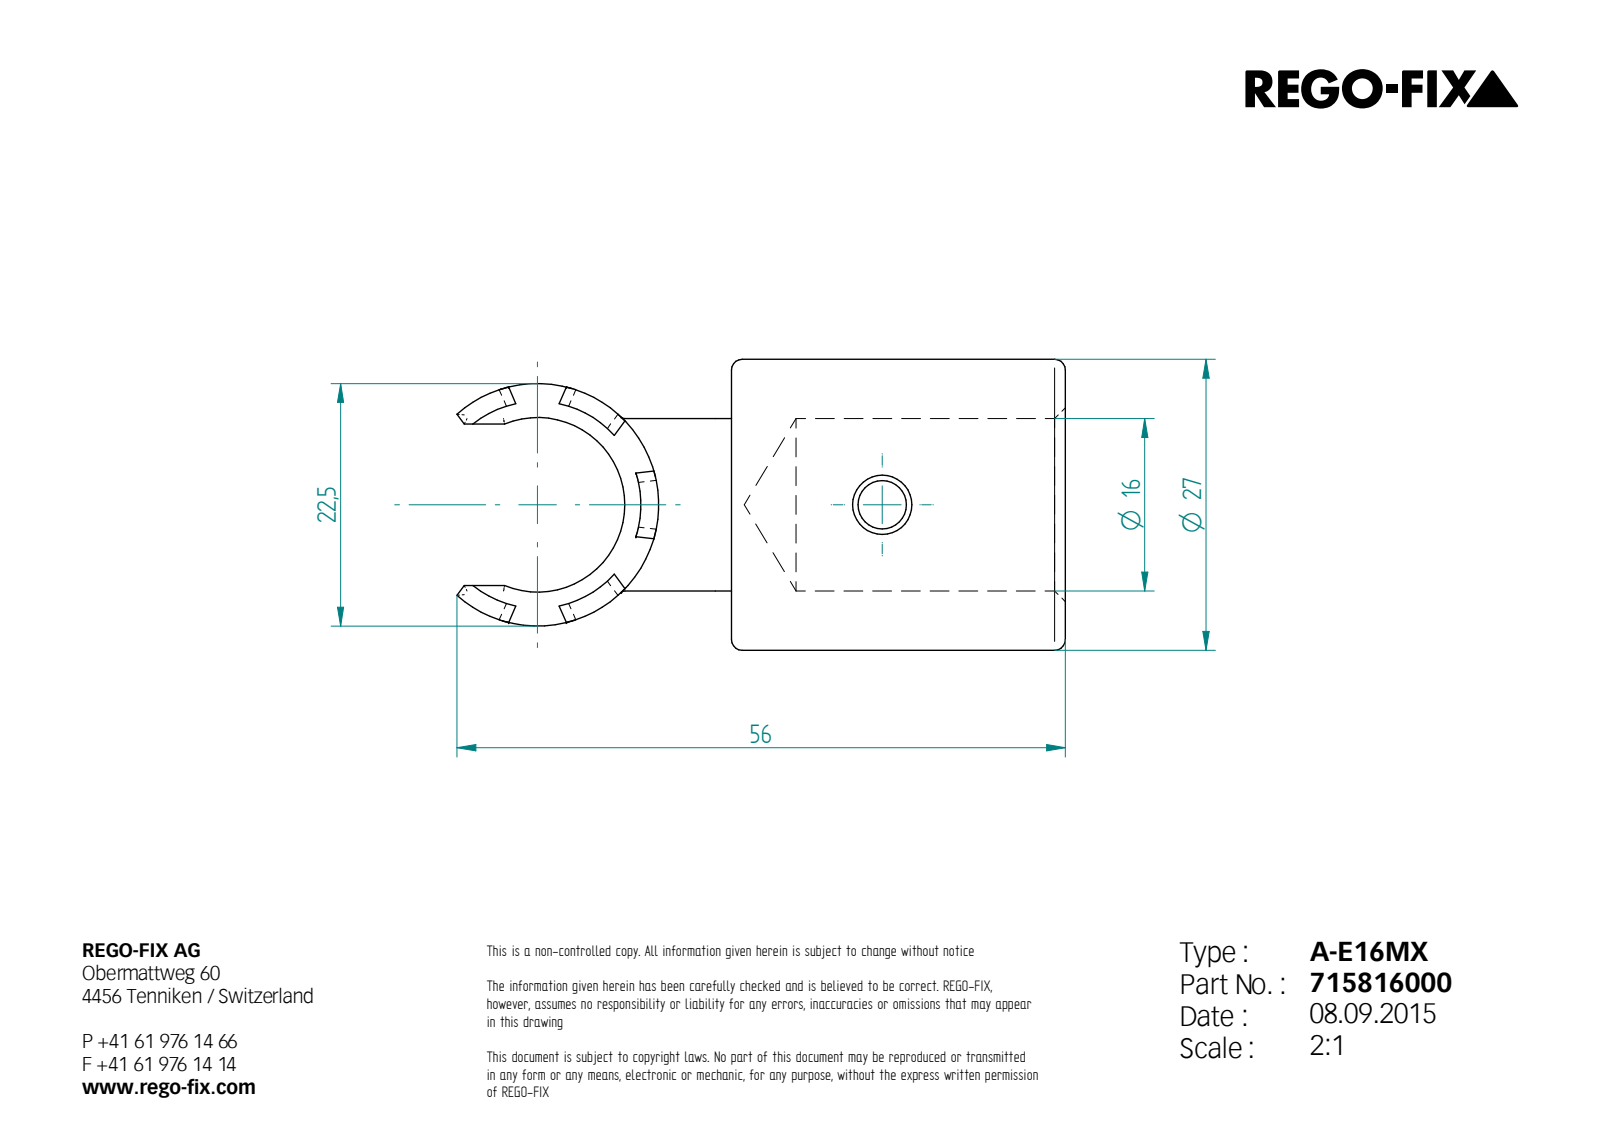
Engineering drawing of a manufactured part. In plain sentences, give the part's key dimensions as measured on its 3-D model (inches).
Its 3-D file was written by "Unknown (AUTOMOTIVE_DESIGN)". It is 1 solid with 72 faces: 26 planar, 29 cylindrical and 17 other. Overall it measures 2.223 by 1.063 by 1.063 inches. Its volume is 0.822 cubic inches and its surface area 9.81 square inches. Round holes: 1 of diameter 0.177, 1 of diameter 0.217, 1 of diameter 0.63. Round bosses or shafts: 1 of diameter 1.063. Partial cylindrical surfaces (rounded edges, fillets, slot ends): 8 of radius 0.035, 4 of radius 0.02, 2 of radius 0.059, 2 of radius 0.079, 1 of radius 0.157, 1 of radius 0.319, 1 of radius 0.378, 1 of radius 0.443. The main face-to-face distances are 1.22, 0.26, 0.157, 0.102, 0.134, 0.236, 0.394, 0.591, 0.079, 0.138.
